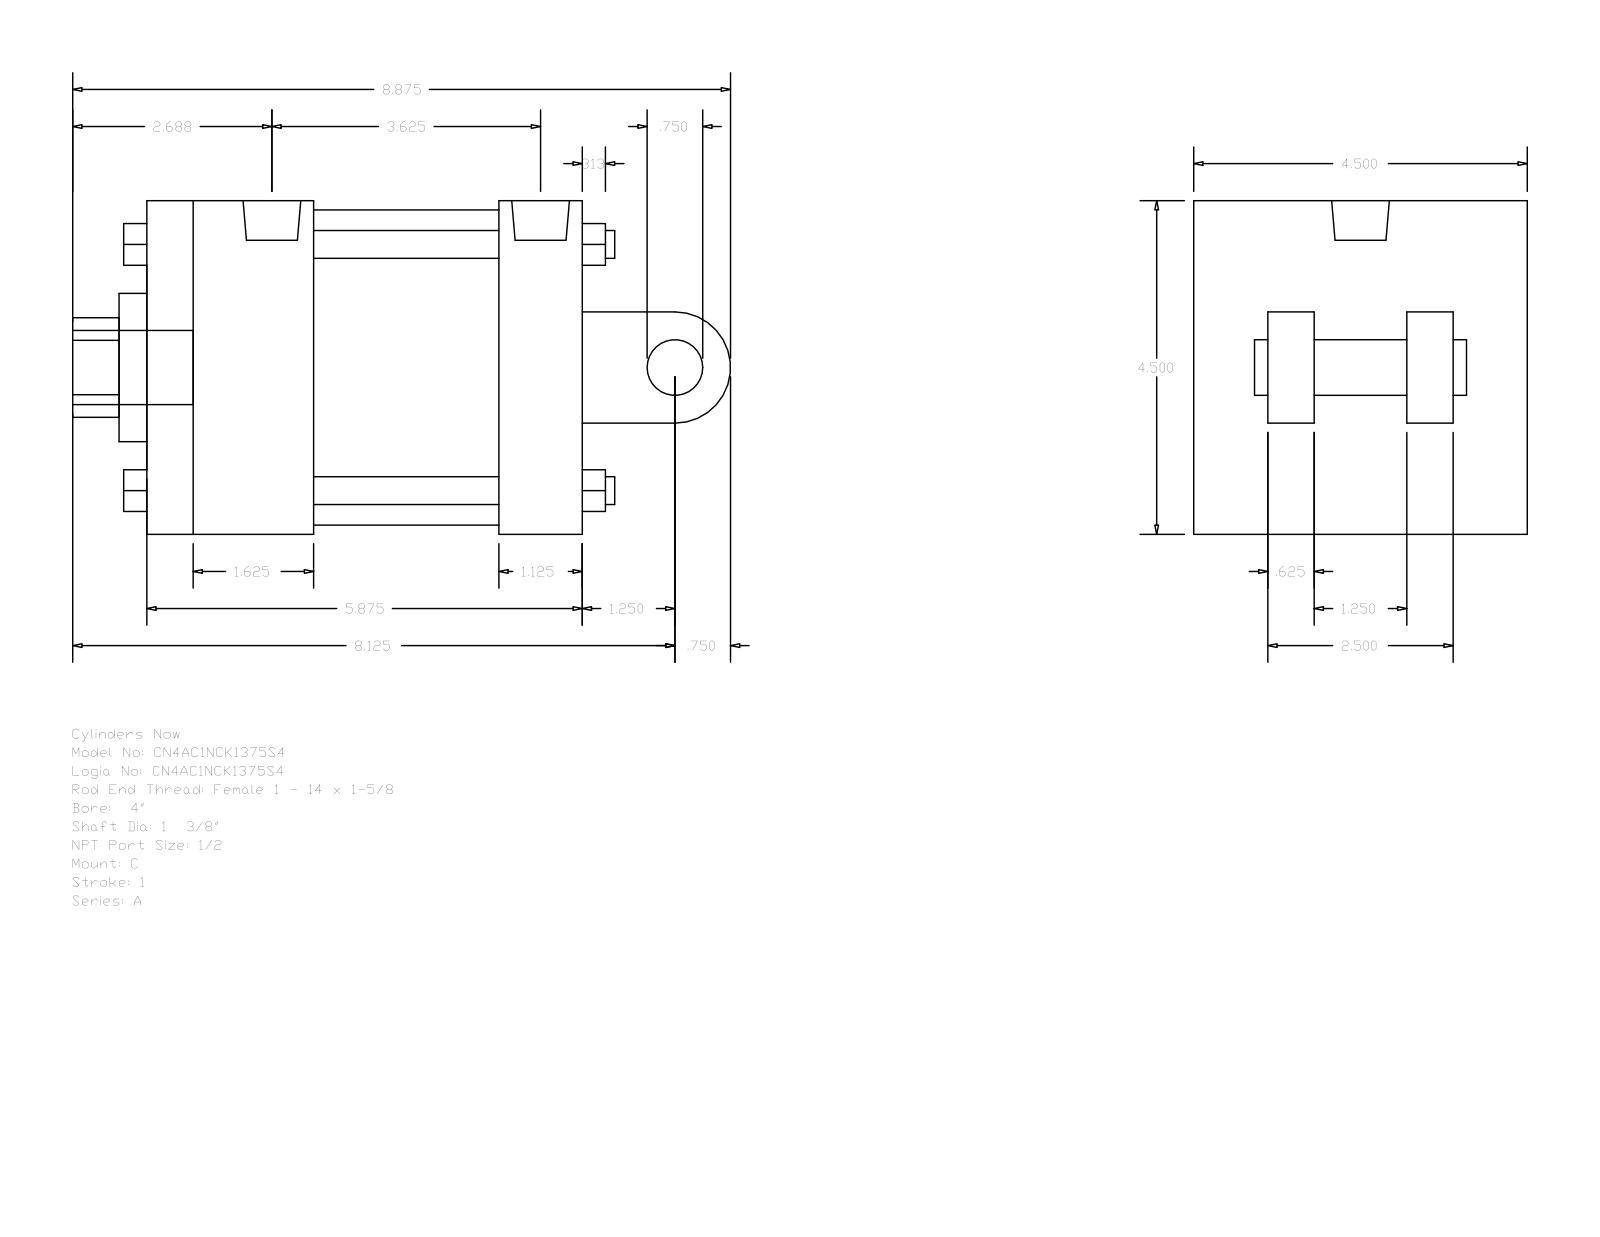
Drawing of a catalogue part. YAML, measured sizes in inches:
part_name: "A_C__0400_1.375"
step_written_by: "GSSL Pune (CONFIG_CONTROL_DESIGN)"
units: inches
bodies: {solids: 0, faces: 135, planar: 102, cylindrical: 33, other: 0}
overall_size: [8.875, 4.5, 4.5]
round_holes:
  - {diameter: 0.344, count: 2}
  - {diameter: 0.778, count: 1}
  - {diameter: 1.375, count: 1}
  - {diameter: 2, count: 1}
  - {diameter: 4.25, count: 1}
round_bosses_or_shafts:
  - {diameter: 0.375, count: 4}
  - {diameter: 0.344, count: 2}
  - {diameter: 1, count: 1}
  - {diameter: 0.778, count: 1}
  - {diameter: 0.75, count: 1}
partial_cylinders:
  - {radius: 0.672, count: 1}
  - {radius: 0.75, count: 1}
face_to_face_distances: [4.5, 5.875, 2.5, 3.625, 2.875, 1.125, 4.75, 2.25, 0.625, 1.625]
hole_center_spacings: [0.125]
